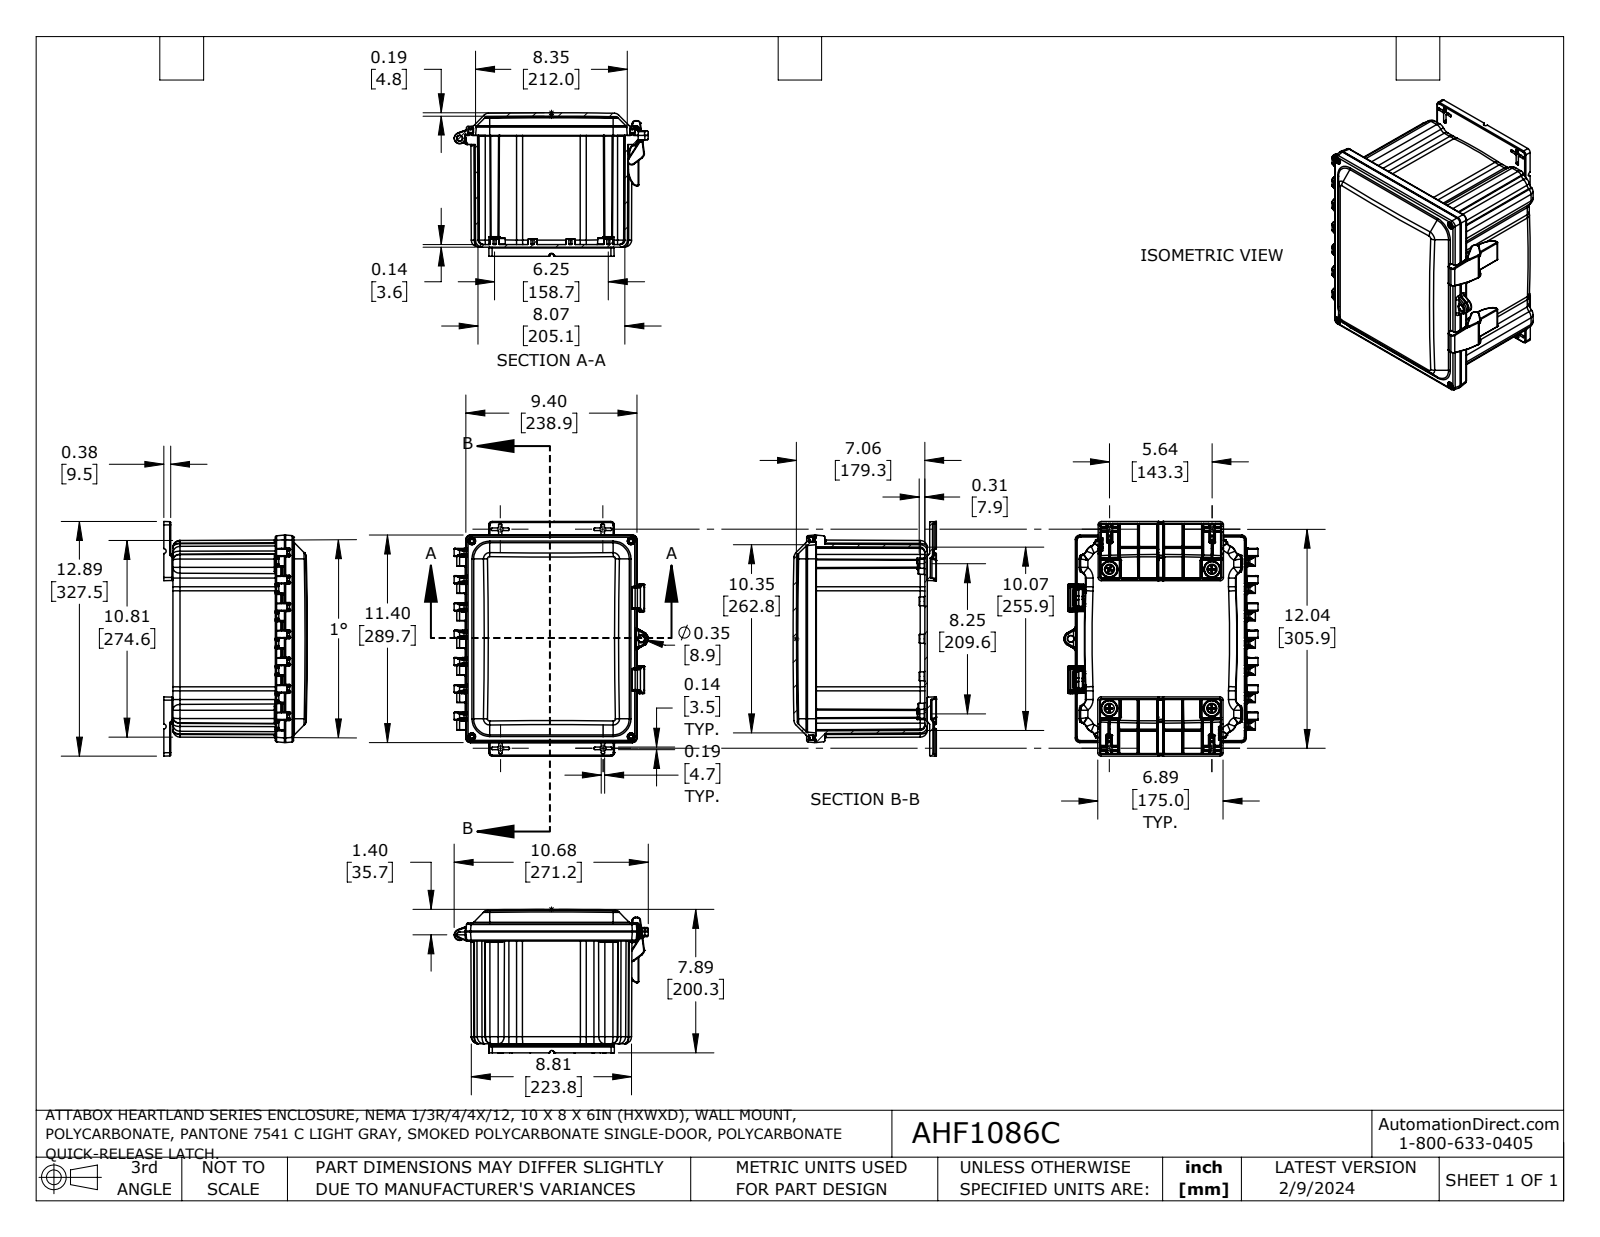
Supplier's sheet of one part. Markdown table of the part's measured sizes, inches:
| quantity | value |
| --- | --- |
| part name | AHF1086C |
| STEP written by | SolidWorks 2023 (AUTOMOTIVE_DESIGN) |
| units | inches |
| bodies | 6 solids, 1625 faces (550 planar, 506 cylindrical, 569 other) |
| overall size | 12.892 × 10.676 × 7.888 |
| volume | 103.6 in³ |
| surface area | 1 146 in² |
| round holes (diameter × count) | 0.187 × 16, 0.195 × 4, 0.25 × 4, 0.28 × 4, 0.39 × 4, 0.27 × 2, 0.327 × 1, 0.375 × 1, 0.45 × 1 |
| round bosses / shafts (diameter × count) | 0.487 × 16, 0.625 × 4, 0.25 × 2, 0.2 × 2, 0.313 × 1 |
| partial cylindrical surfaces (radius × count) | 0.035 × 178, 0.065 × 23, 0.01 × 22, 0.02 × 21, 0.338 × 16, 0.05 × 8, 0.413 × 8, 0.09 × 4 |
| main face-to-face distances | 0.115, 0.14, 8.115, 0.5, 6.14, 0.29, 10.115, 6, 8, 6.64 |
| hole center spacings | 2.931, 2.063, 4.649, 2.083, 4.167, 4.621, 4.125, 5.863 |
